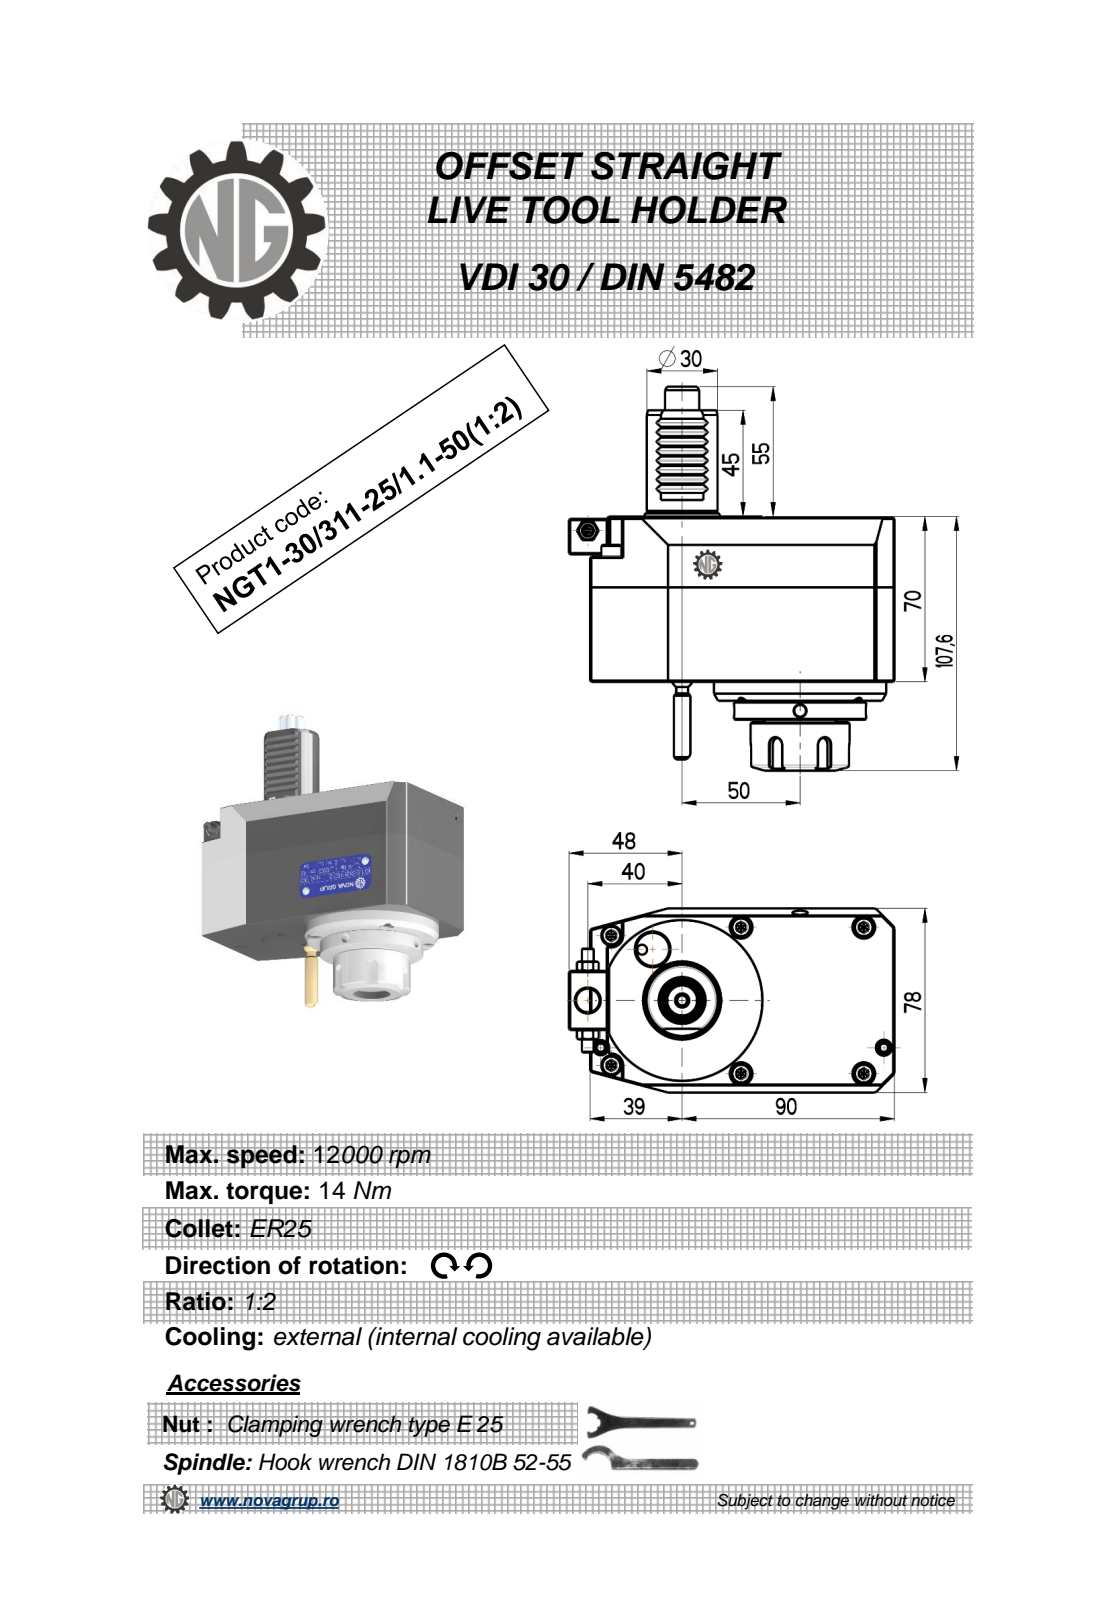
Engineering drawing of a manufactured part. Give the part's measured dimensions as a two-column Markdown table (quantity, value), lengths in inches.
| quantity | value |
| --- | --- |
| part name | NGT1_30_311_25_1_1_50_1_2 |
| STEP written by | PRO/ENGINEER BY PARAMETRIC TECHNOLOGY CORPORATION, 2010280 (CONFIG_CONTROL_DESIGN) |
| units | inches |
| bodies | 1 solid, 415 faces (152 planar, 123 cylindrical, 140 other) |
| overall size | 6.402 × 5.433 × 3.071 |
| volume | 47.64 in³ |
| surface area | 99.34 in² |
| round holes (diameter × count) | 0.165 × 2, 0.197 × 2, 0.098 × 1, 0.118 × 1, 0.374 × 1, 0.394 × 1, 0.551 × 1 |
| round bosses / shafts (diameter × count) | 0.315 × 2, 0.197 × 2, 2.874 × 1, 2.205 × 1, 1.654 × 1, 1.299 × 1, 1.181 × 1, 0.736 × 1 |
| partial cylindrical surfaces (radius × count) | 0.115 × 16, 0.006 × 12, 0.01 × 12, 0.012 × 8, 0.118 × 5, 0.177 × 2, 0.224 × 1, 0.285 × 1 |
| main face-to-face distances | 3.071, 2.756, 0.315, 5.079, 0.63, 3.386, 0.02, 2.717, 0.295, 3.091 |
| hole center spacings | 0.492, 0.846, 0.984, 1.378, 1.575, 1.788, 2.904, 4.644 |
